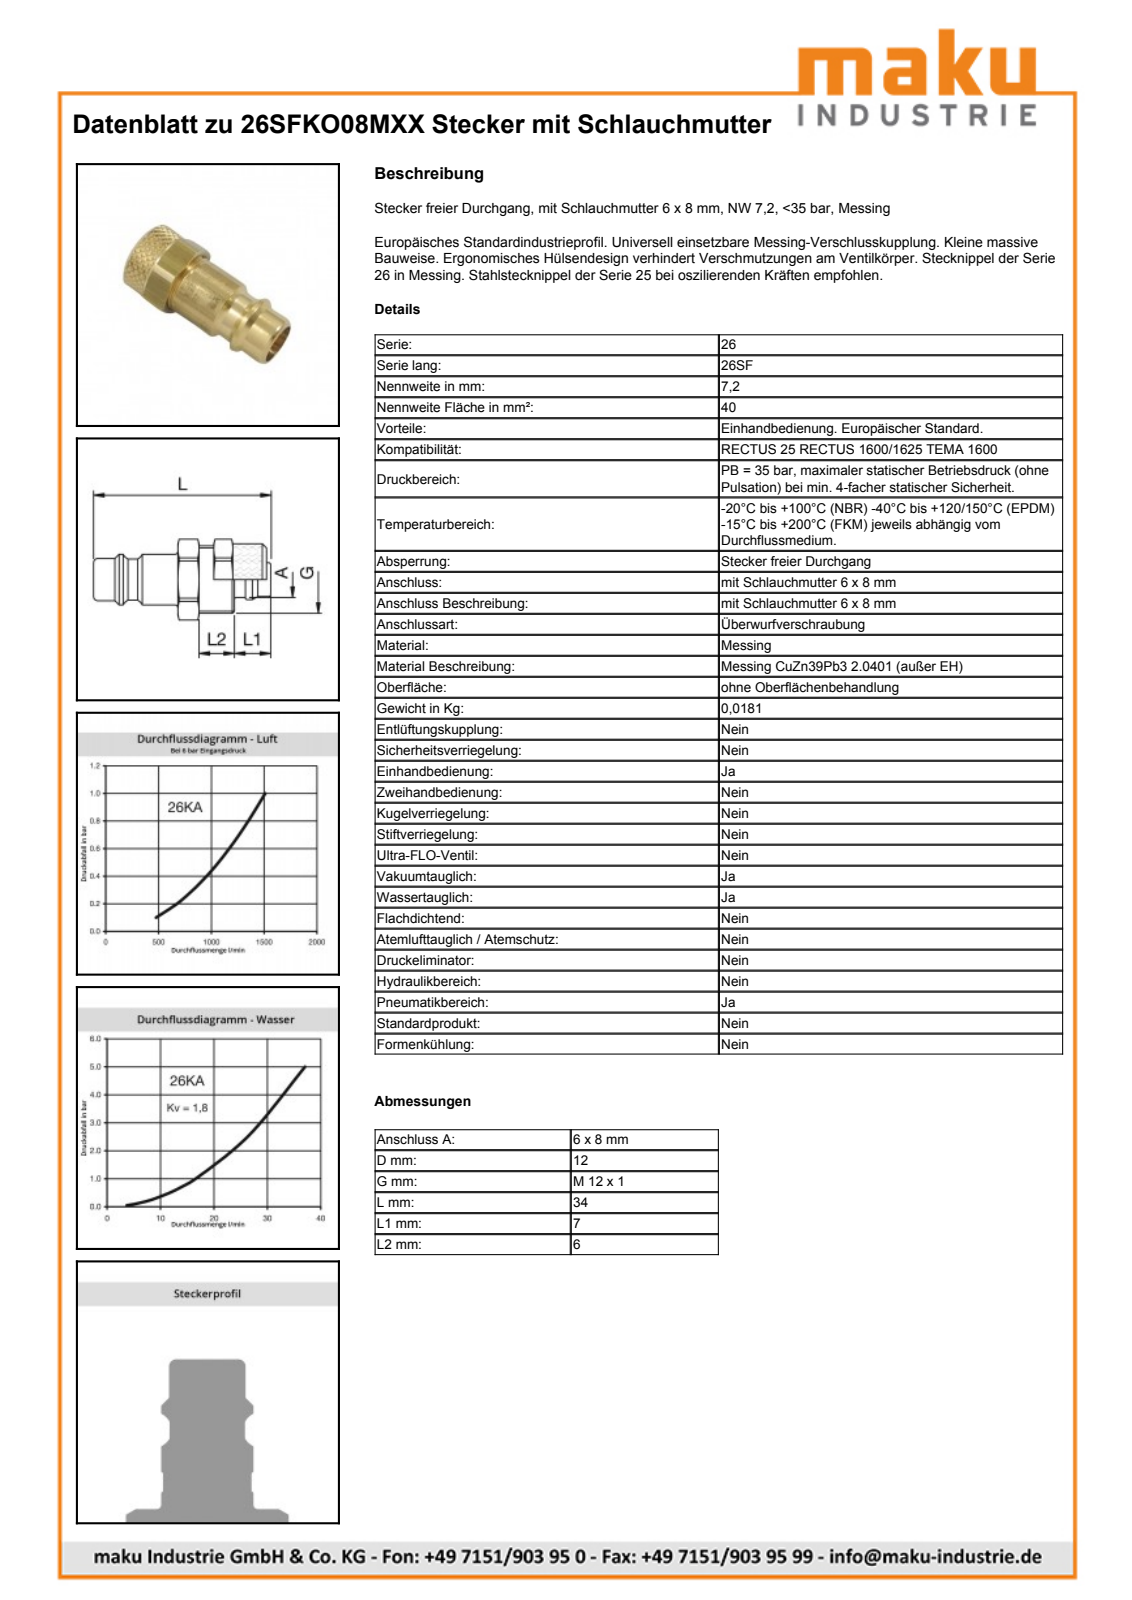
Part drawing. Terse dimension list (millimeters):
name: D102975; D102672; D102238
written by: Autodesk Inventor 2011 (AUTOMOTIVE_DESIGN)
unit: mm
bodies: 2 solids, 64 faces (18 planar, 18 cylindrical, 28 other)
size: 34 × 15.47 × 14.79
volume: 2 338 mm³; area: 3 034 mm²
holes: 1× ⌀4.9, 1× ⌀7.85, 1× ⌀8.25, 1× ⌀10.92
bosses: 1× ⌀14.15, 1× ⌀12, 1× ⌀10.6, 1× ⌀10, 1× ⌀9.75, 1× ⌀6.7, 1× ⌀6.05
rounds: 1× R7.75
face distances: 14, 6.25, 11, 4.75, 0.85, 7.1, 11.85, 4, 3.15, 3.1
